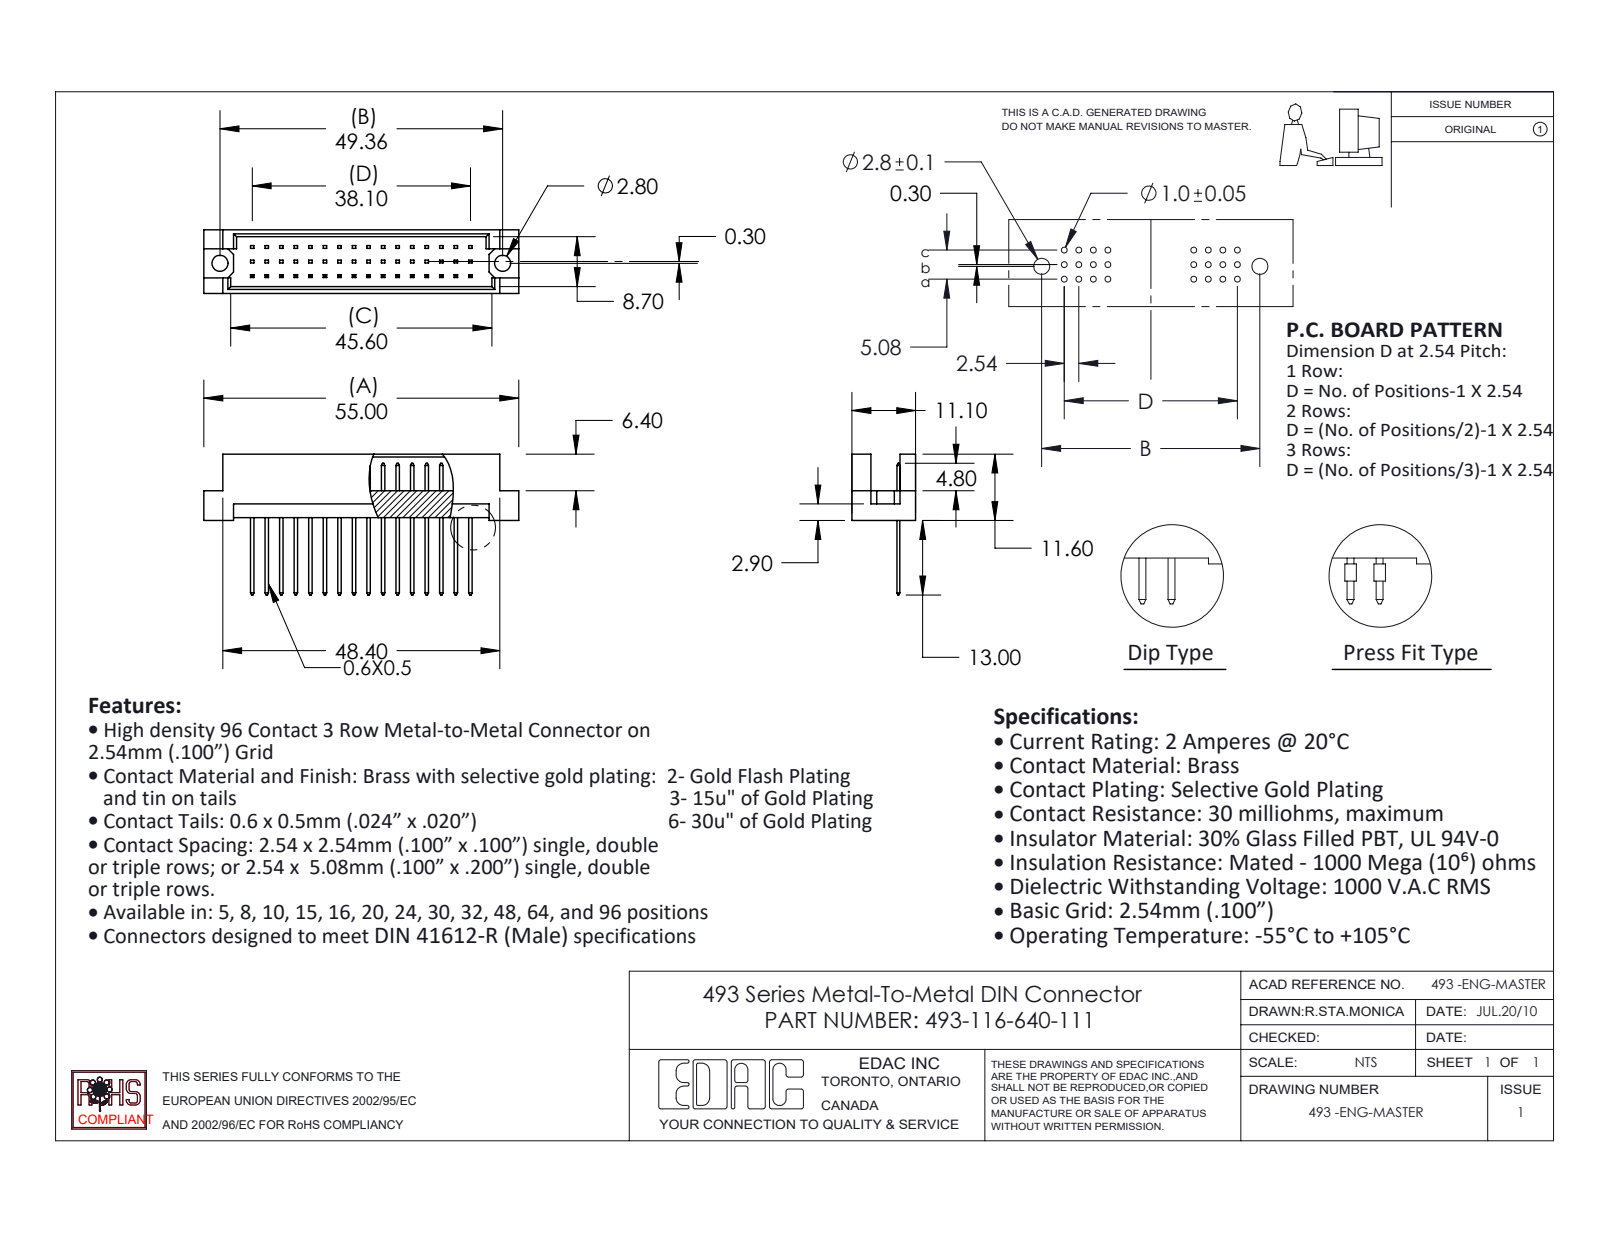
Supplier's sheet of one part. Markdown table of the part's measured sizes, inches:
| quantity | value |
| --- | --- |
| part name | 493-290_40; 493-116-640-111; 493 Part_48 |
| STEP written by | SolidWorks 2020 (CONFIG_CONTROL_DESIGN) |
| units | inches |
| bodies | 17 solids, 468 faces (464 planar, 4 cylindrical, 0 other) |
| overall size | 2.165 × 0.969 × 0.437 |
| volume | 0.206 in³ |
| surface area | 7.068 in² |
| round holes (diameter × count) | 0.11 × 2 |
| main face-to-face distances | 0.047, 0.39, 0.437, 0.02, 0.343, 0.1, 0.185, 0.2, 0.109, 0.328 |
| hole center spacings | 1.943 |
